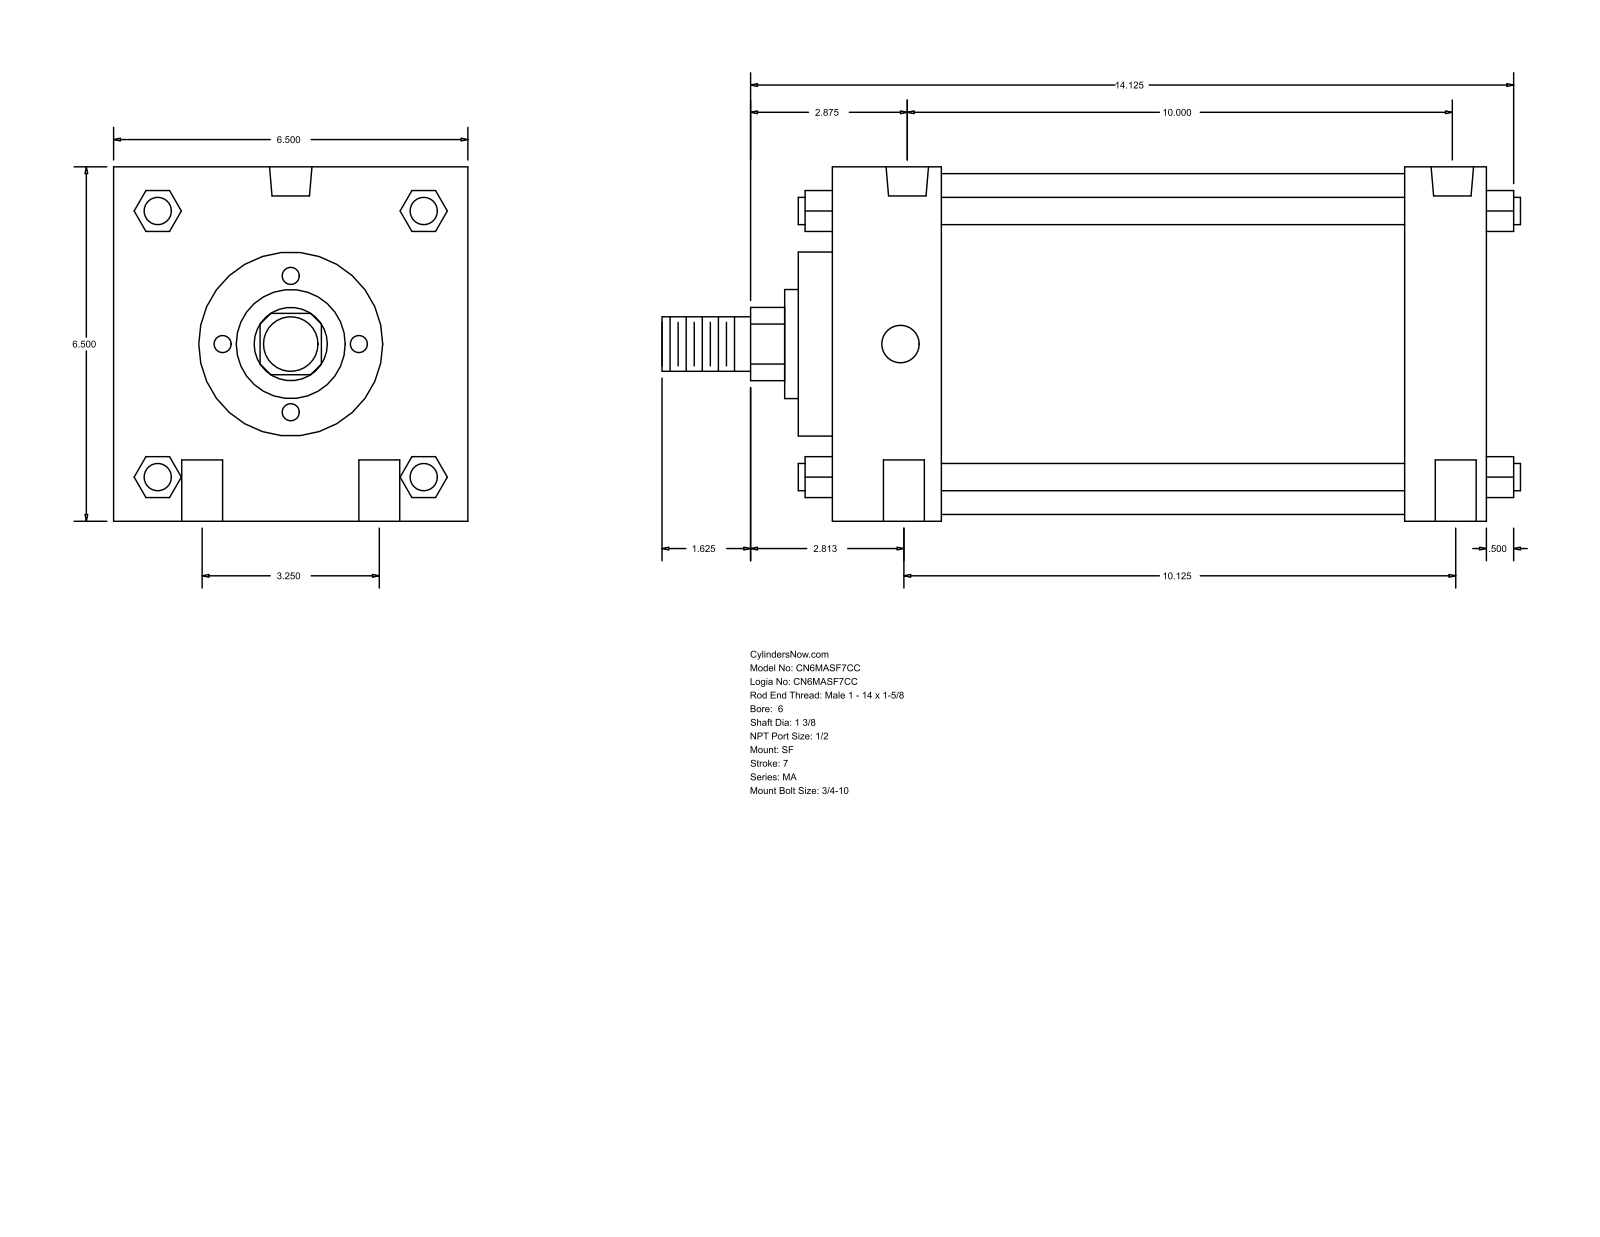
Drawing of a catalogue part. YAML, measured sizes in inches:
part_name: "MA_SF__0600_1.375"
step_written_by: "GSSL Pune (CONFIG_CONTROL_DESIGN)"
units: inches
bodies: {solids: 0, faces: 126, planar: 95, cylindrical: 31, other: 0}
overall_size: [15.75, 6.5, 6.5]
round_holes:
  - {diameter: 0.75, count: 4}
  - {diameter: 0.687, count: 2}
  - {diameter: 0.778, count: 2}
round_bosses_or_shafts:
  - {diameter: 0.5, count: 4}
  - {diameter: 6.25, count: 1}
  - {diameter: 3.375, count: 1}
  - {diameter: 2, count: 1}
  - {diameter: 1.375, count: 1}
  - {diameter: 1, count: 1}
partial_cylinders:
  - {radius: 0.672, count: 1}
face_to_face_distances: [6.5, 12, 10.5, 2, 1.5, 8.5, 10, 2.625, 0.625, 12.625]
hole_center_spacings: [1.626, 10.193, 3.25, 10.125, 10.633, 10, 10]
